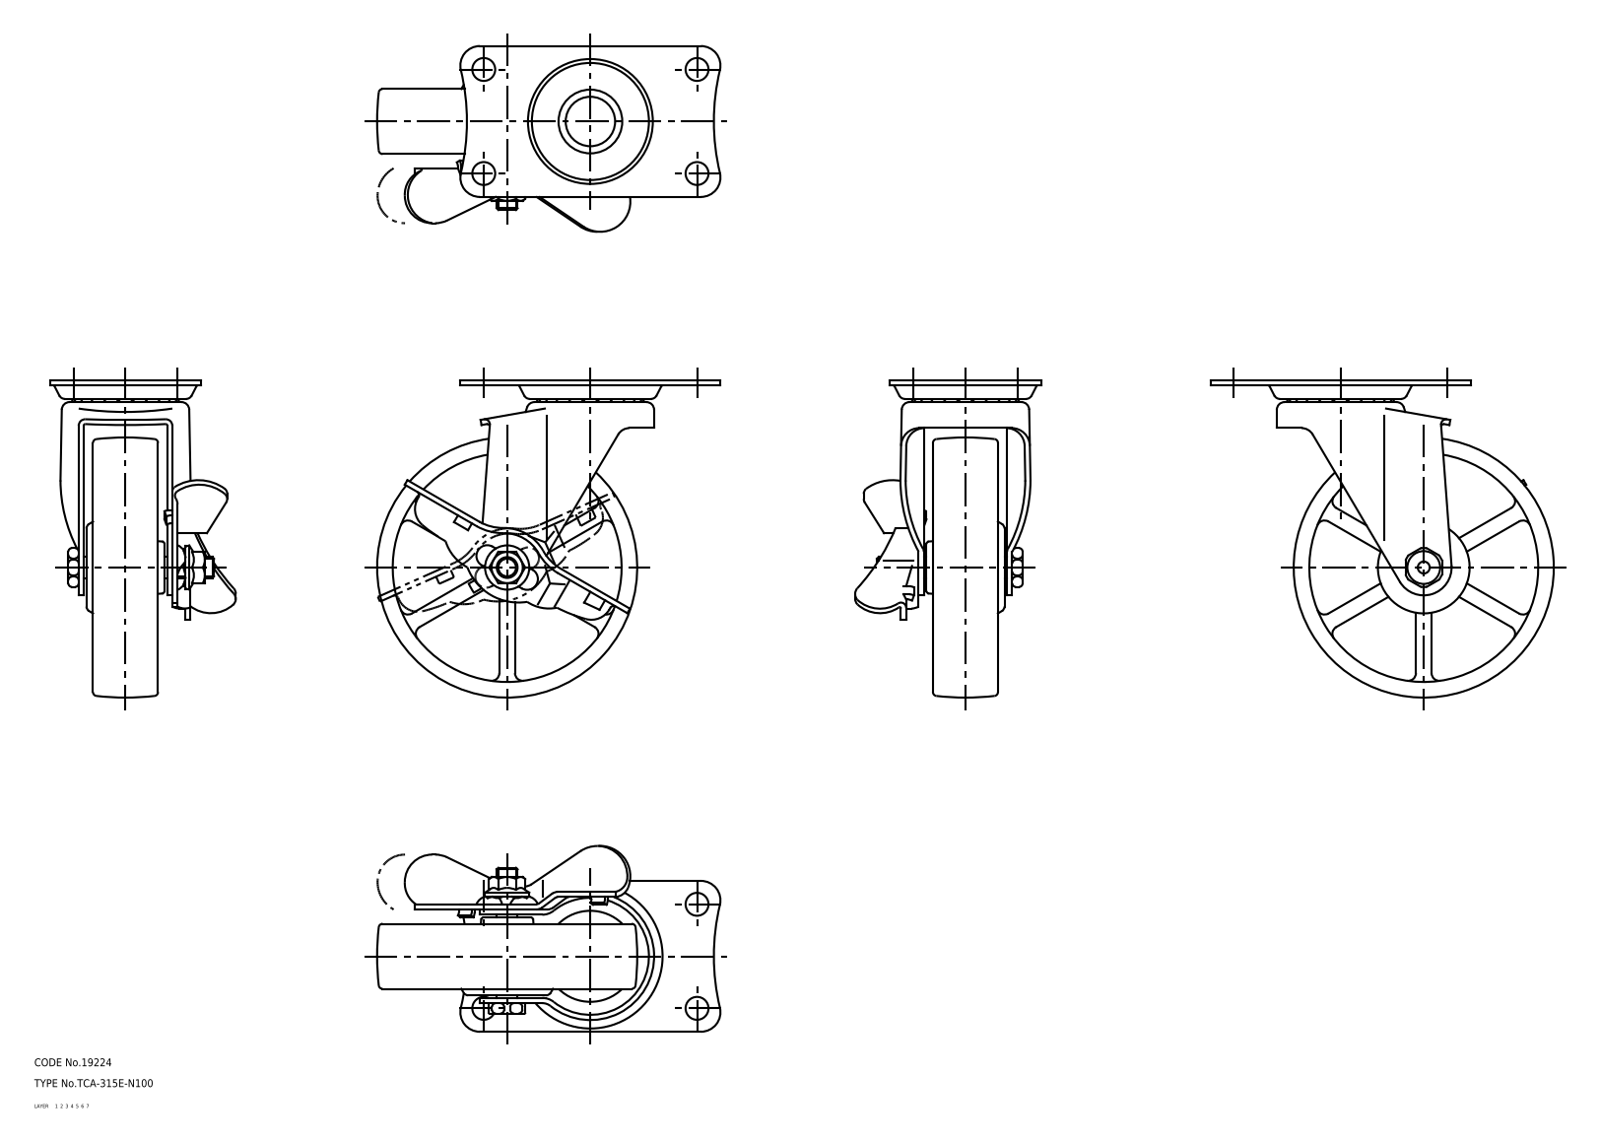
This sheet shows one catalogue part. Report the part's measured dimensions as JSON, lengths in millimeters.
{"part_name": "lever; wheel; mounting plate; main shaft (+2 more)", "step_written_by": "CADfix (AUTOMOTIVE_DESIGN)", "units": "millimeters", "bodies": {"solids": 6, "faces": 803, "planar": 0, "cylindrical": 0, "other": 803}, "overall_size": [132, 122, 71.4], "volume_mm3": 190123, "surface_area_mm2": 71981}
